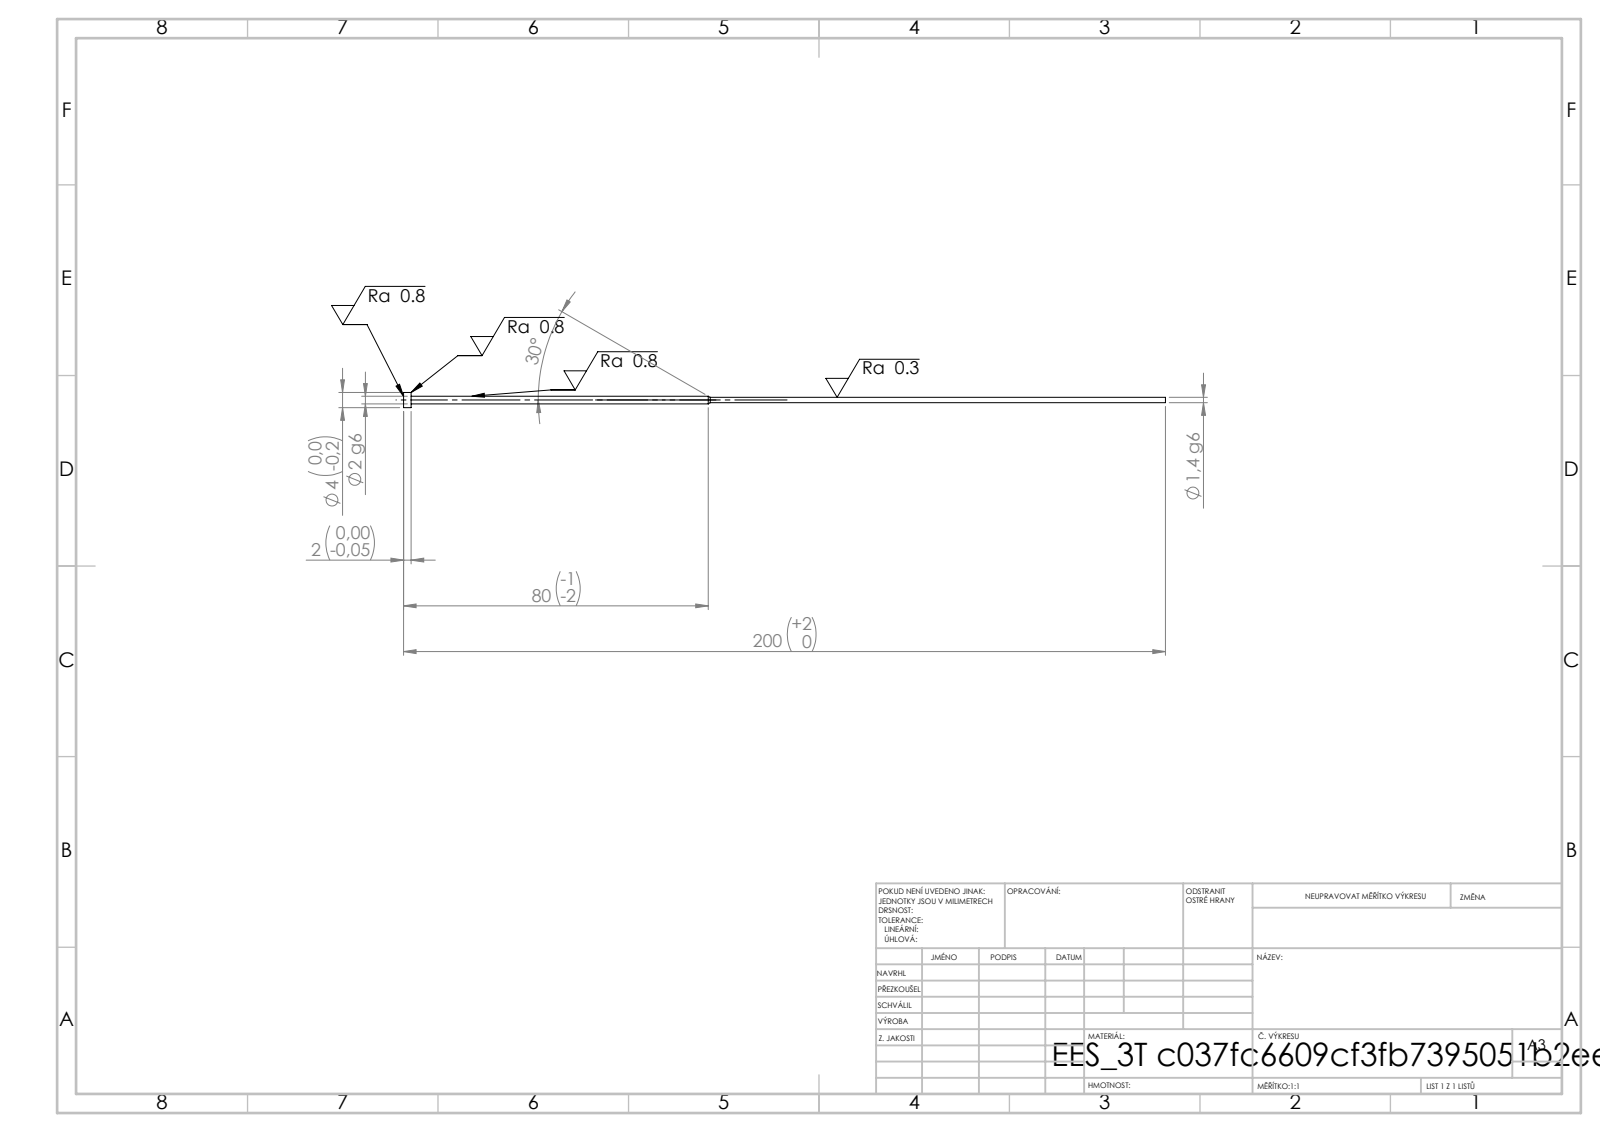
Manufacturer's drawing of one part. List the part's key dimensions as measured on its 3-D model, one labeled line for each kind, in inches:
STEP written by: SolidWorks 2019 (CONFIG_CONTROL_DESIGN)
Units: inches
Bodies: 1 solid, 11 faces (3 planar, 6 cylindrical, 2 other)
Overall size (bounding box): 7.874 × 0.157 × 0.157
Volume: 0.028 in³ · Surface area: 1.654 in²
Round bosses / shafts (diameter × count): ⌀0.157 ×1, ⌀0.079 ×1, ⌀0.055 ×1
Main face-to-face distances: 0.079, 7.795, 7.874
